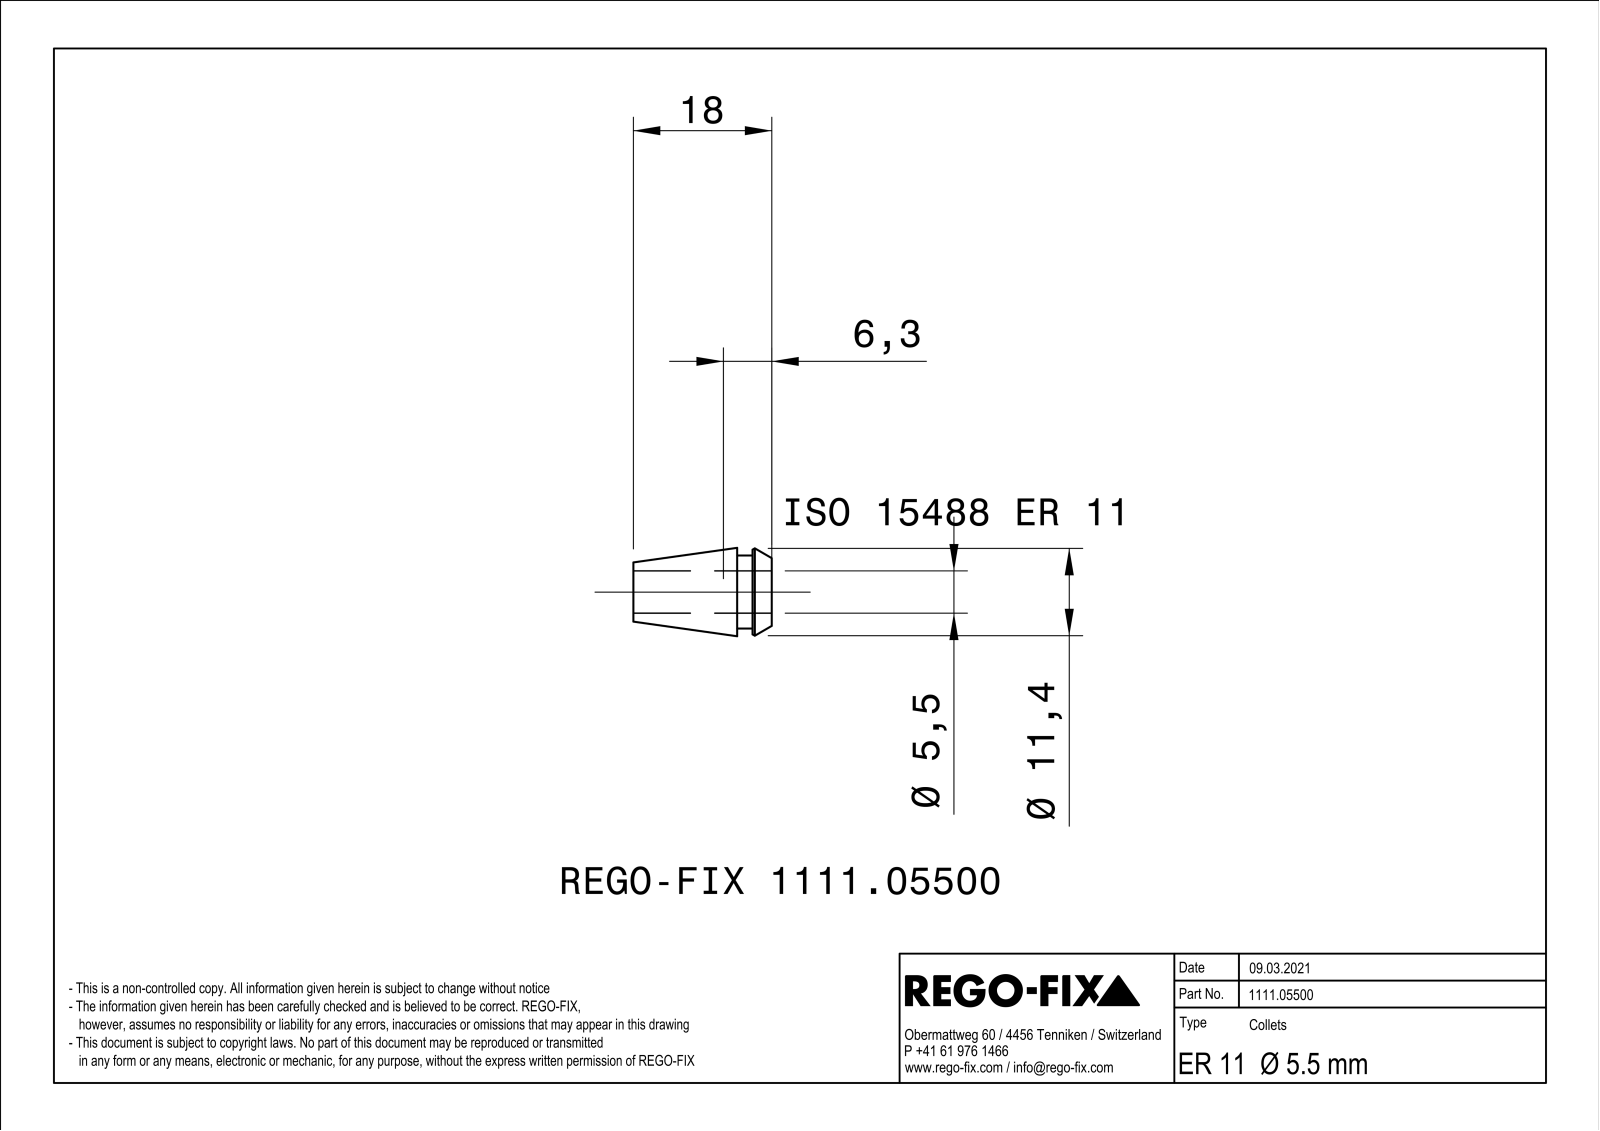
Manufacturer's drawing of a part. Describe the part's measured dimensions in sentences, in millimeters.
The part is named "NOCUT". Its 3-D file was written by "SIEMENS PLM Software Solid Edge ST10 (AUTOMOTIVE_DESIGN)". It is 1 solid with 157 faces: 66 planar, 37 cylindrical and 54 other. Overall it measures 18 by 11.5 by 11.49 millimeters. Its volume is 747 cubic millimeters and its surface area 1 565 square millimeters. Round holes: 1 of diameter 5.5. Round bosses or shafts: 1 of diameter 11.5, 1 of diameter 9.5. Partial cylindrical surfaces (rounded edges, fillets, slot ends): 12 of radius 25. The main face-to-face distances are 0.45, 0.46, 0.44, 2.5, 4.5, 2, 18, 15.5, 13.5, 4.
